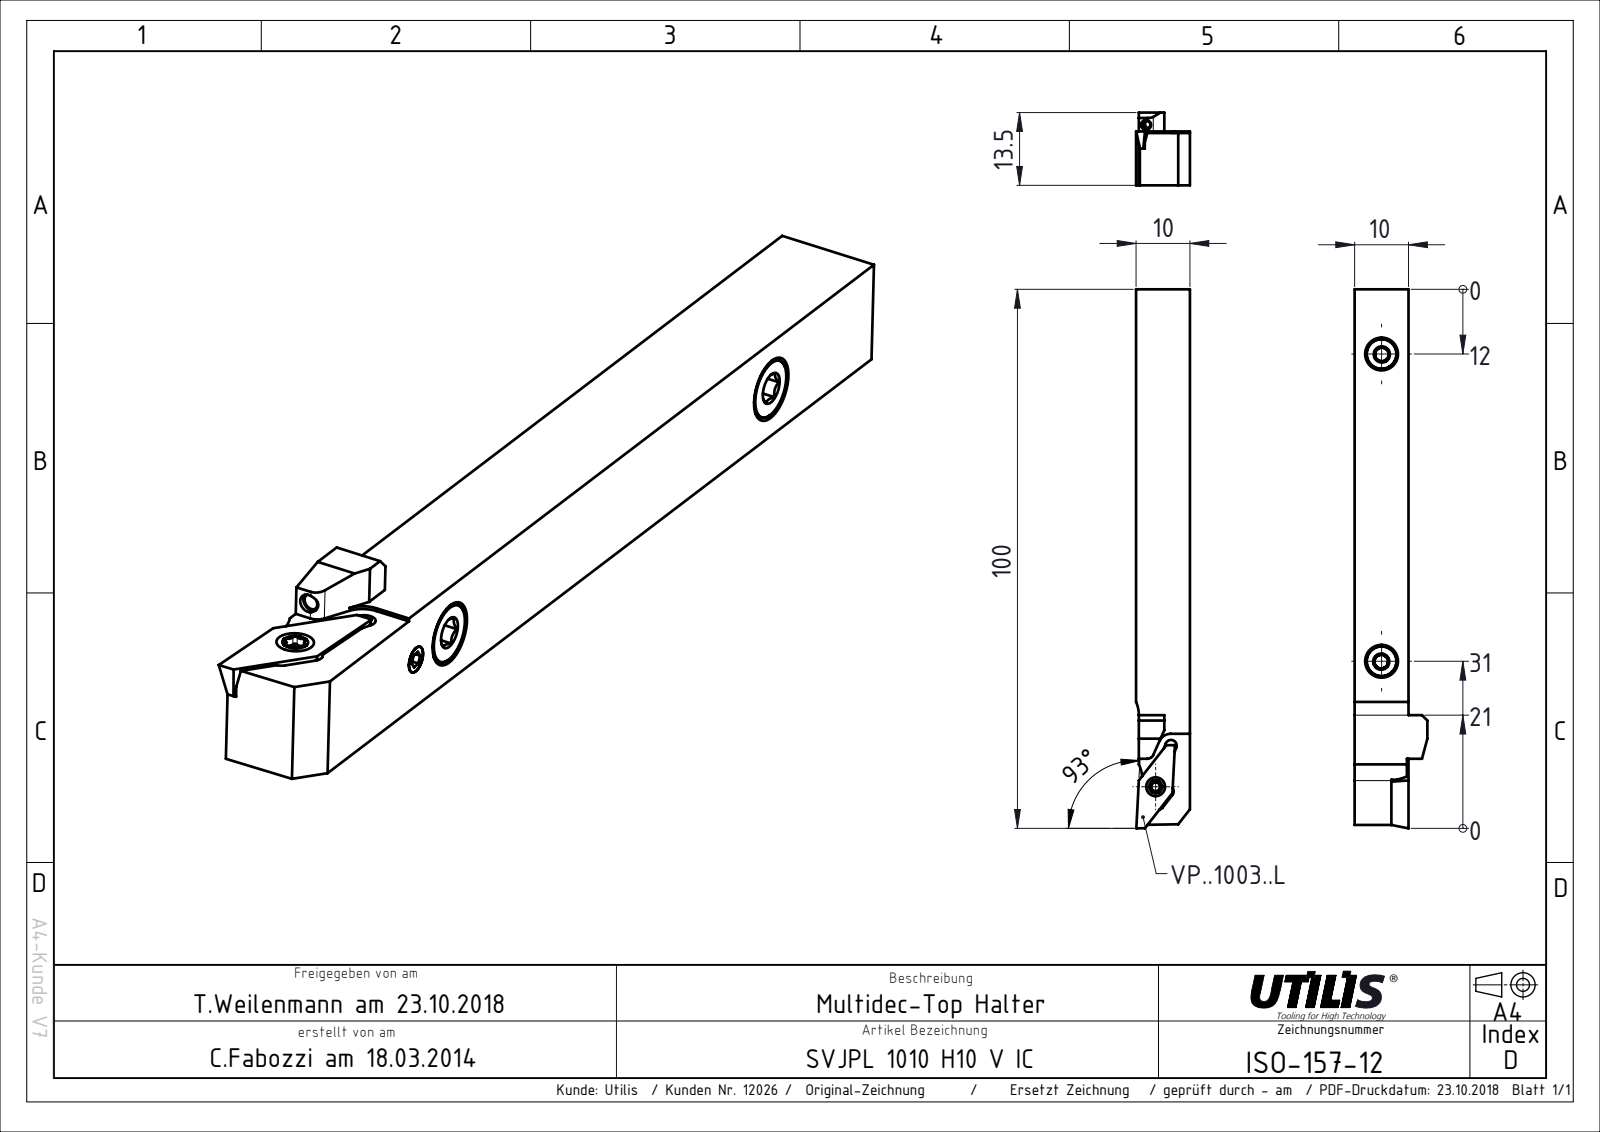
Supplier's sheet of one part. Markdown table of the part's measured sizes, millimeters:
| quantity | value |
| --- | --- |
| part name | ISO-157-12 |
| STEP written by | SolidWorks 2015 (AUTOMOTIVE_DESIGN) |
| units | millimeters |
| bodies | 1 solid, 57 faces (50 planar, 7 cylindrical, 0 other) |
| overall size | 100 × 13.5 × 10.2 |
| volume | 9 874 mm³ |
| surface area | 4 322 mm² |
| partial cylindrical surfaces (radius × count) | 1.05 × 3, 6.1 × 2, 2.3 × 1 |
| main face-to-face distances | 10, 9.73, 9.7, 5, 13.5, 3.8, 3.5, 6.82, 2.88, 3.18 |
